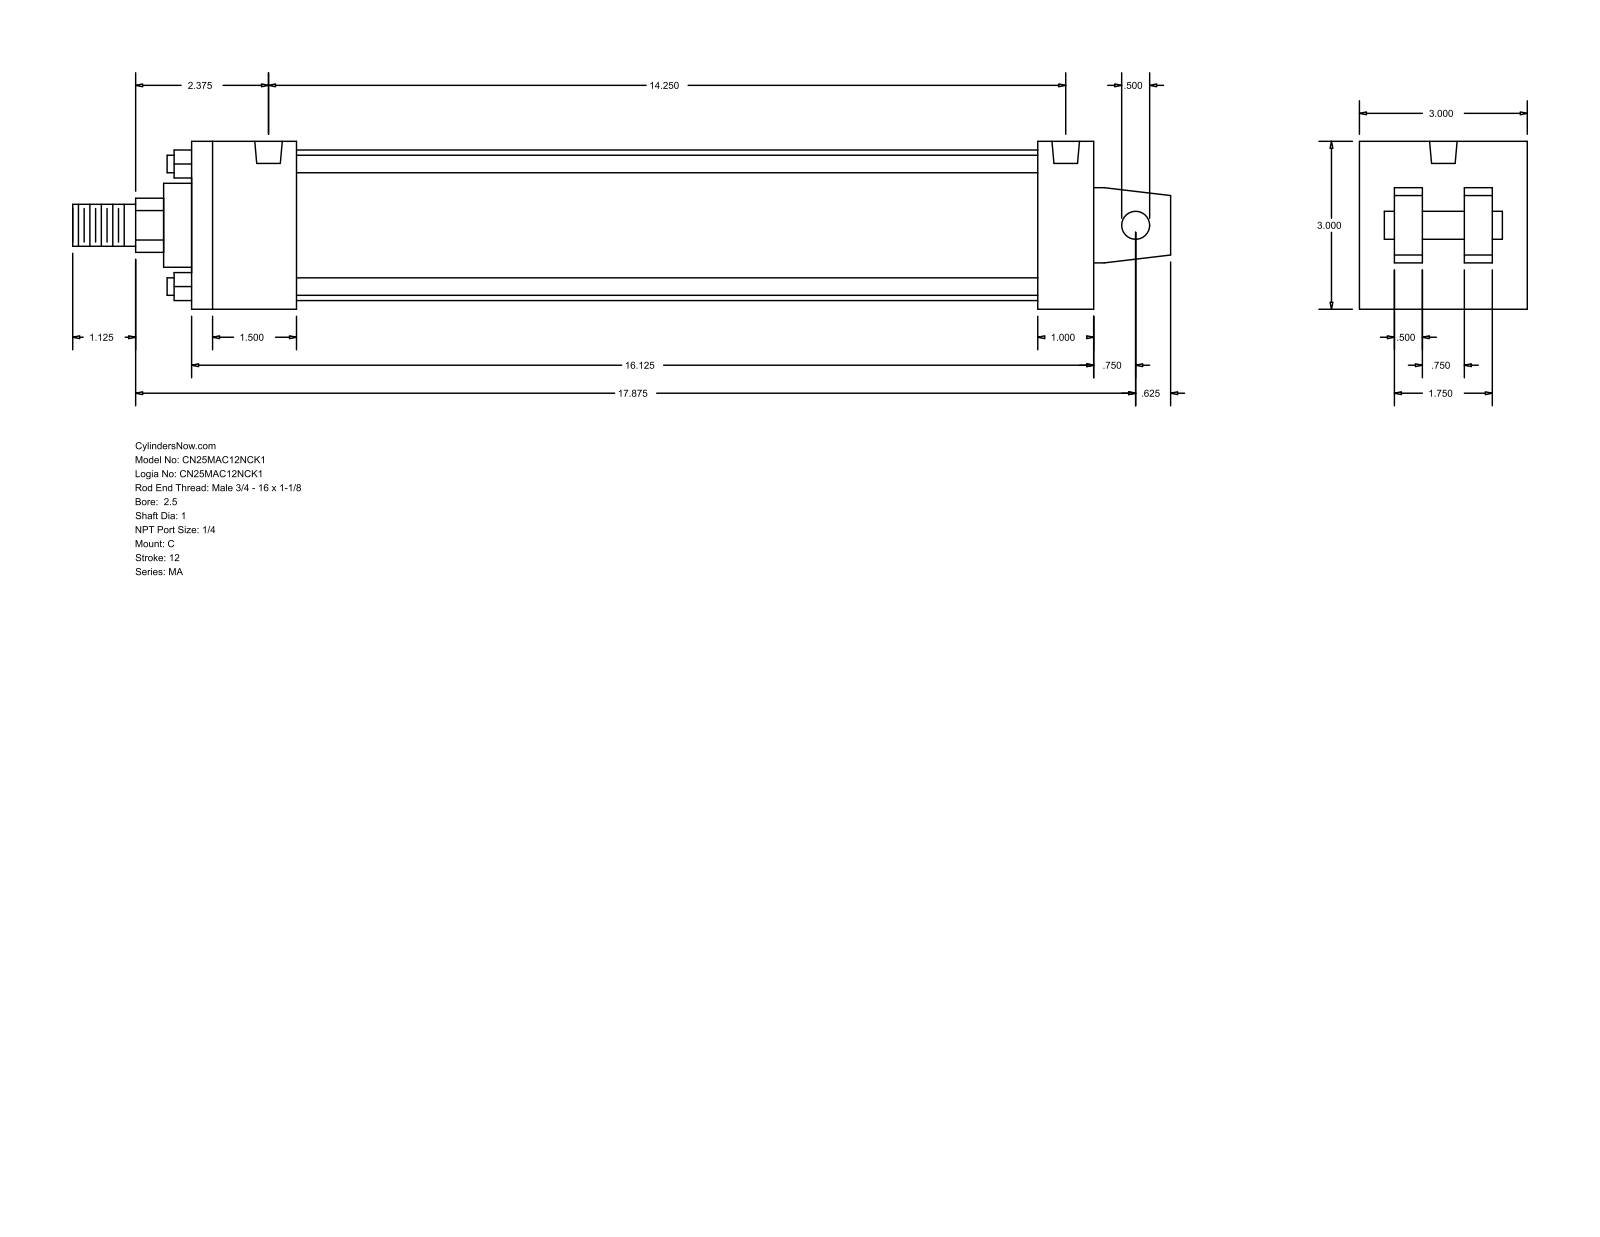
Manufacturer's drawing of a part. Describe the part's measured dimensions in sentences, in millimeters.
The part is named "MA_C__0250_1". Its 3-D file was written by "GSSL Pune (CONFIG_CONTROL_DESIGN)". It is 0 solids with 103 faces: 76 planar, 27 cylindrical and 0 other. Overall it measures 498.48 by 76.2 by 76.2 millimeters. Round holes: 4 of diameter 7.94, 2 of diameter 12.49. Round bosses or shafts: 4 of diameter 7.94, 1 of diameter 68.33, 1 of diameter 38.1, 1 of diameter 25.4, 1 of diameter 19.05, 1 of diameter 12.7. Partial cylindrical surfaces (rounded edges, fillets, slot ends): 1 of radius 12.29. The main face-to-face distances are 76.2, 47.63, 409.58, 12.7, 60.33, 15.87, 28.57, 384.17, 336.54, 361.95. The hole center spacings are 361.94.
